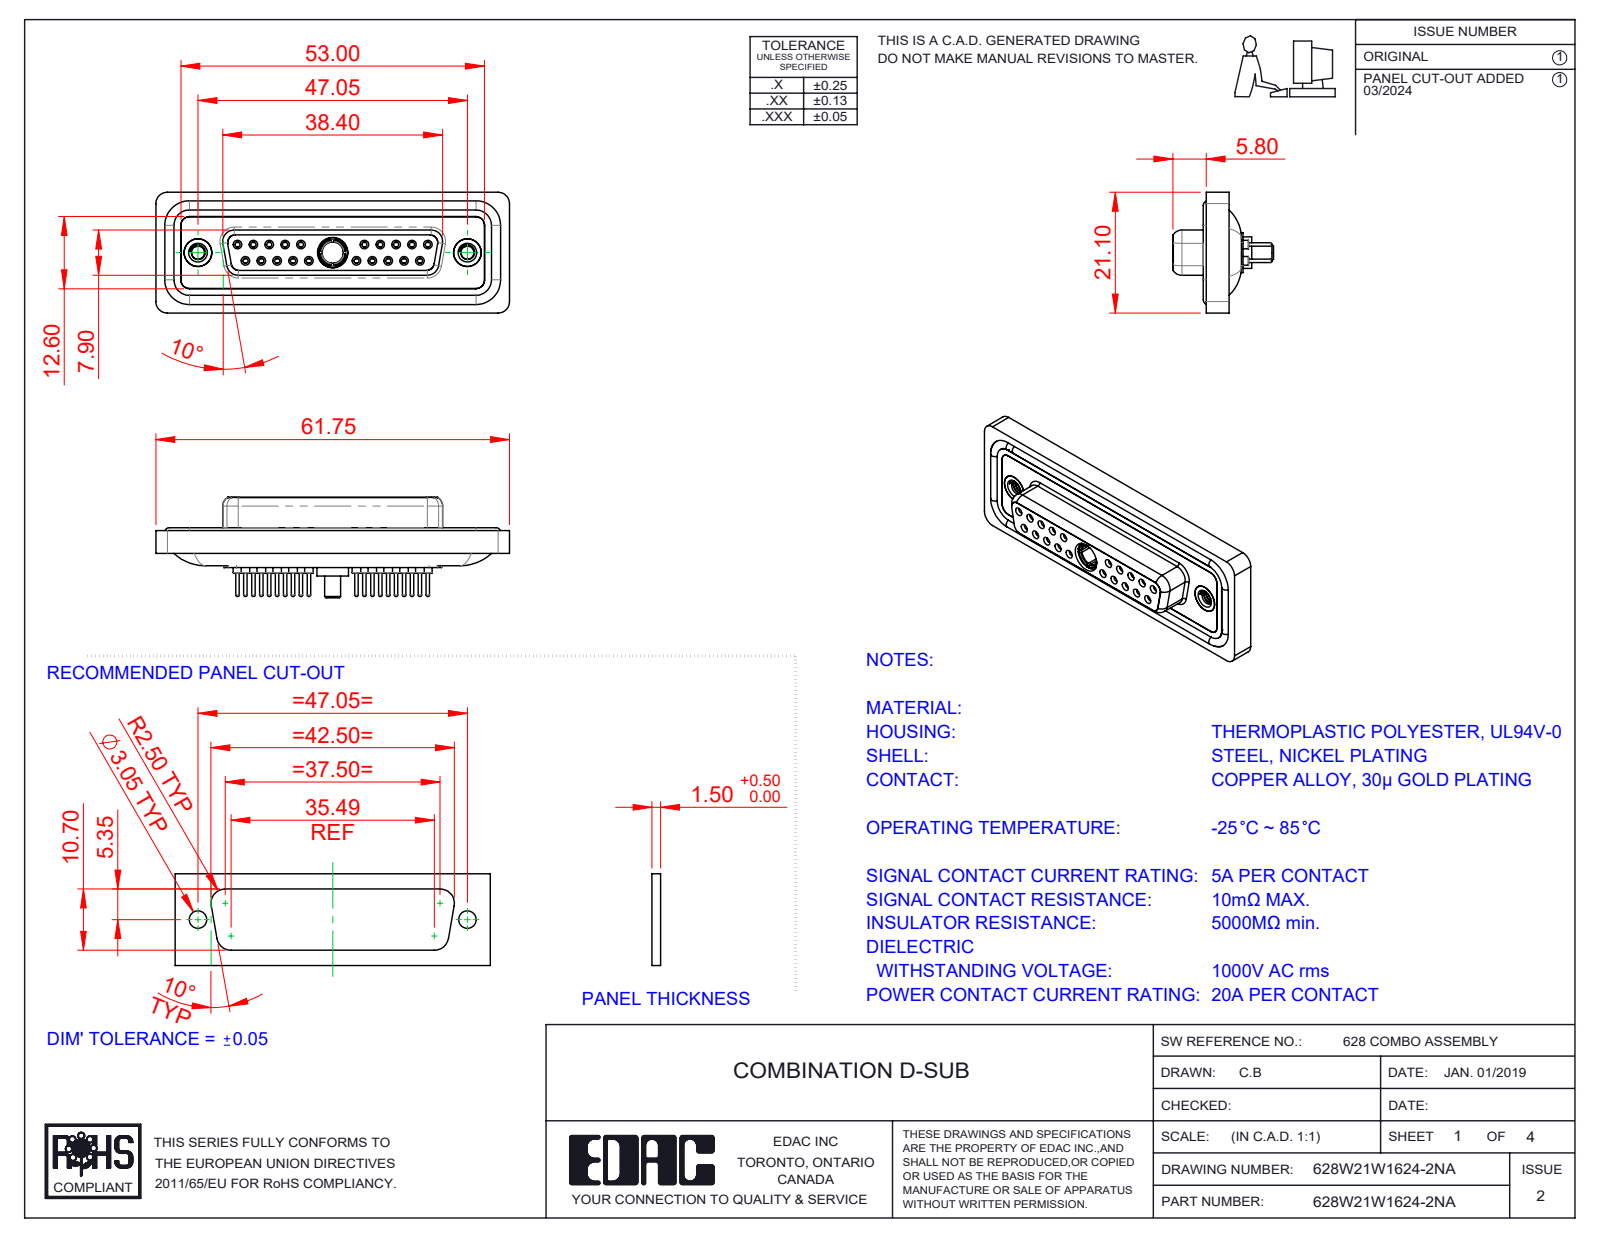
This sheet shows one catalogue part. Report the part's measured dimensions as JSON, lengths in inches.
{"part_name": "628Combo Threaded Rivet_A; 628Combo Shell Front_25 Contacts; 628Combo Contact Row 2_24; 628W21W1624-2NA (+5 more)", "step_written_by": "SolidWorks 2023 (CONFIG_CONTROL_DESIGN)", "units": "inches", "bodies": {"solids": 29, "faces": 1558, "planar": 434, "cylindrical": 593, "other": 531}, "overall_size": [2.431, 0.831, 0.691], "volume_in3": 0.511, "surface_area_in2": 21.7, "round_holes": [[0.035, 20], [0.043, 20], [0.059, 20], [0.079, 20], [0.063, 10], [0.067, 10], [0.191, 3], [0.089, 2], [0.157, 2], [0.159, 2], [0.197, 2], [0.146, 1]], "round_bosses_or_shafts": [[0.087, 20], [0.024, 20], [0.063, 14], [0.195, 2], [0.189, 2], [0.217, 1], [0.205, 1], [0.195, 1]], "partial_cylinders_radius": [[0.059, 22], [0.079, 18], [0.053, 8], [0.063, 8], [0.01, 4], [0.02, 4], [0.024, 4], [0.026, 4]], "face_to_face_distances": [0.016, 0.071, 0.293, 0.26, 0.222, 0.02, 0.063, 0.278, 0.114, 0.043], "hole_center_spacings": [0.124, 0.109, 0.218, 0.198, 0.327, 0.294, 0.654, 0.763]}
